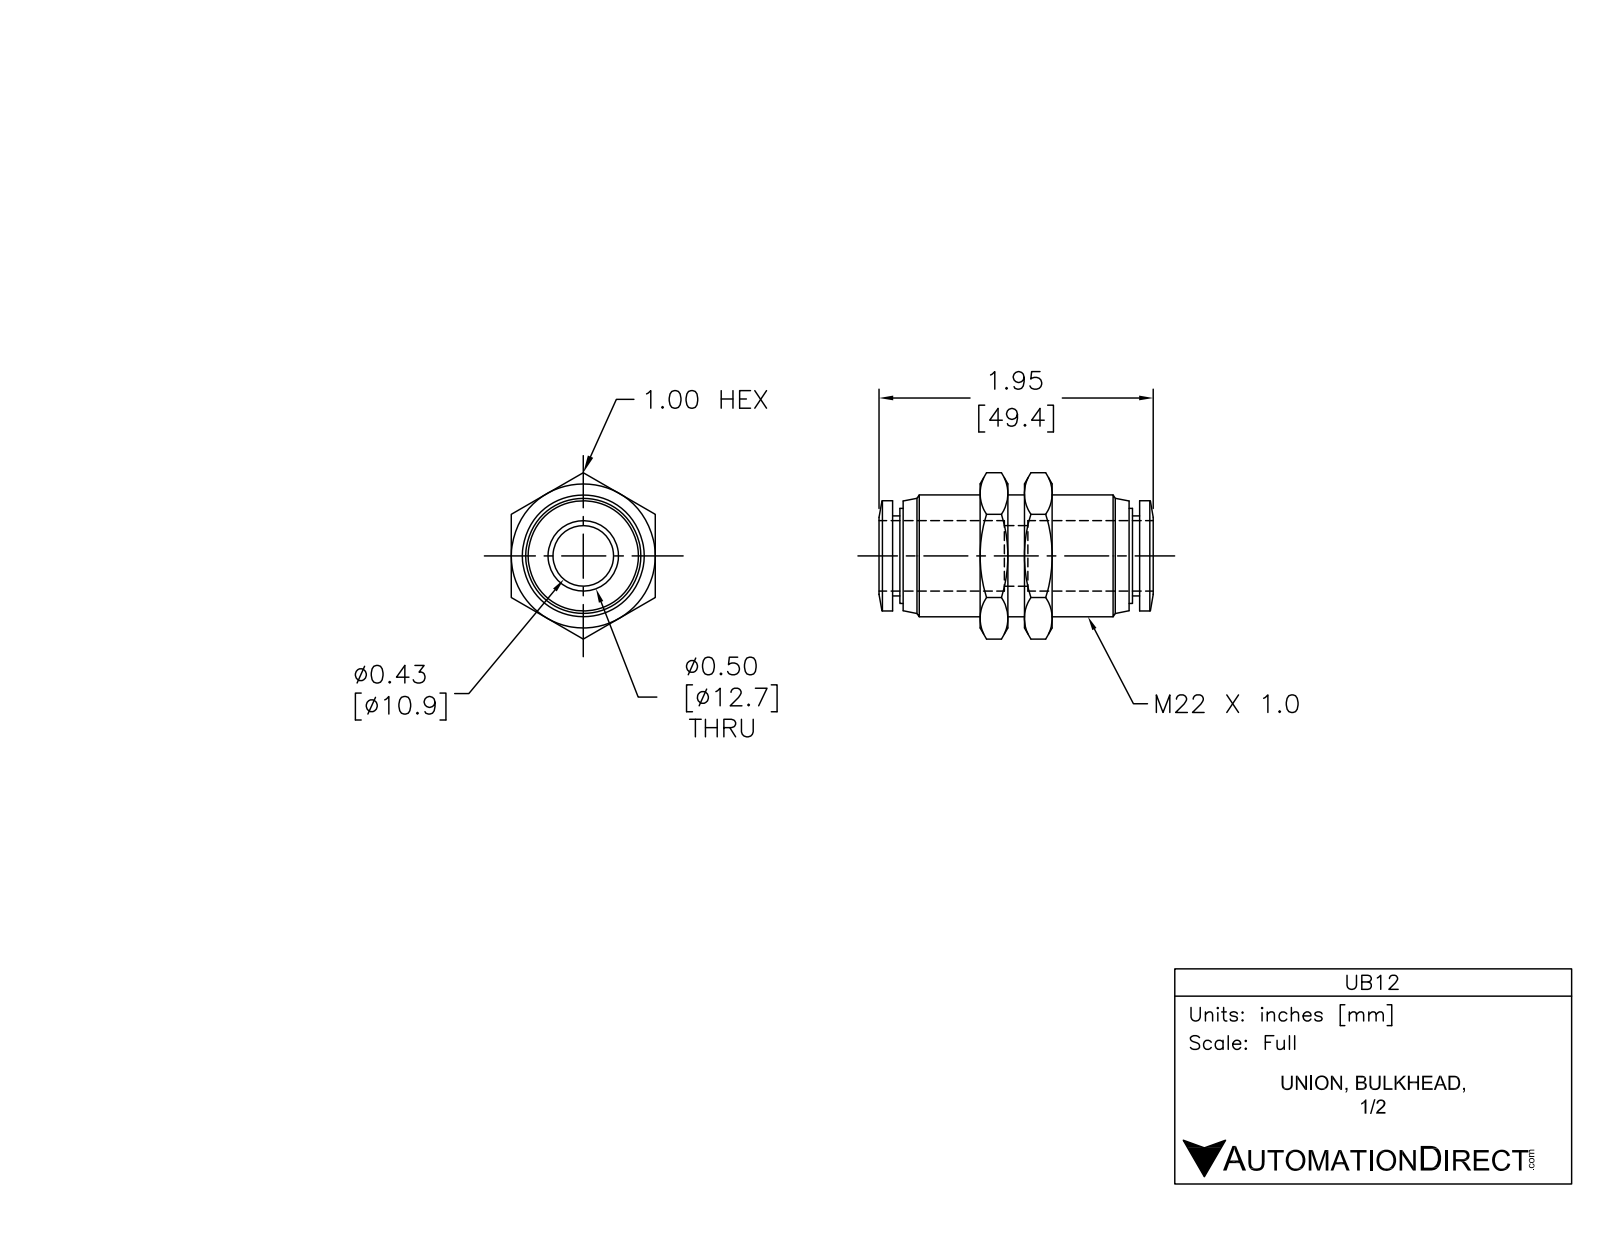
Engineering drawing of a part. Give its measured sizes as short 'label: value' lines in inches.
name: UB12
written by: SolidWorks 2015 (AUTOMOTIVE_DESIGN)
unit: in
bodies: 1 solid, 96 faces (24 planar, 24 cylindrical, 48 other)
size: 1.949 × 1.182 × 1.024
volume: 0.79 in³; area: 11.11 in²
holes: 1× ⌀0.433, 1× ⌀0.51
bosses: 1× ⌀0.866, 1× ⌀0.783, 1× ⌀0.675, 1× ⌀0.569
face distances: 1.024, 0.197, 0.315, 0.622, 0.819, 0.937, 1.134, 0.075, 1.681, 0.547
